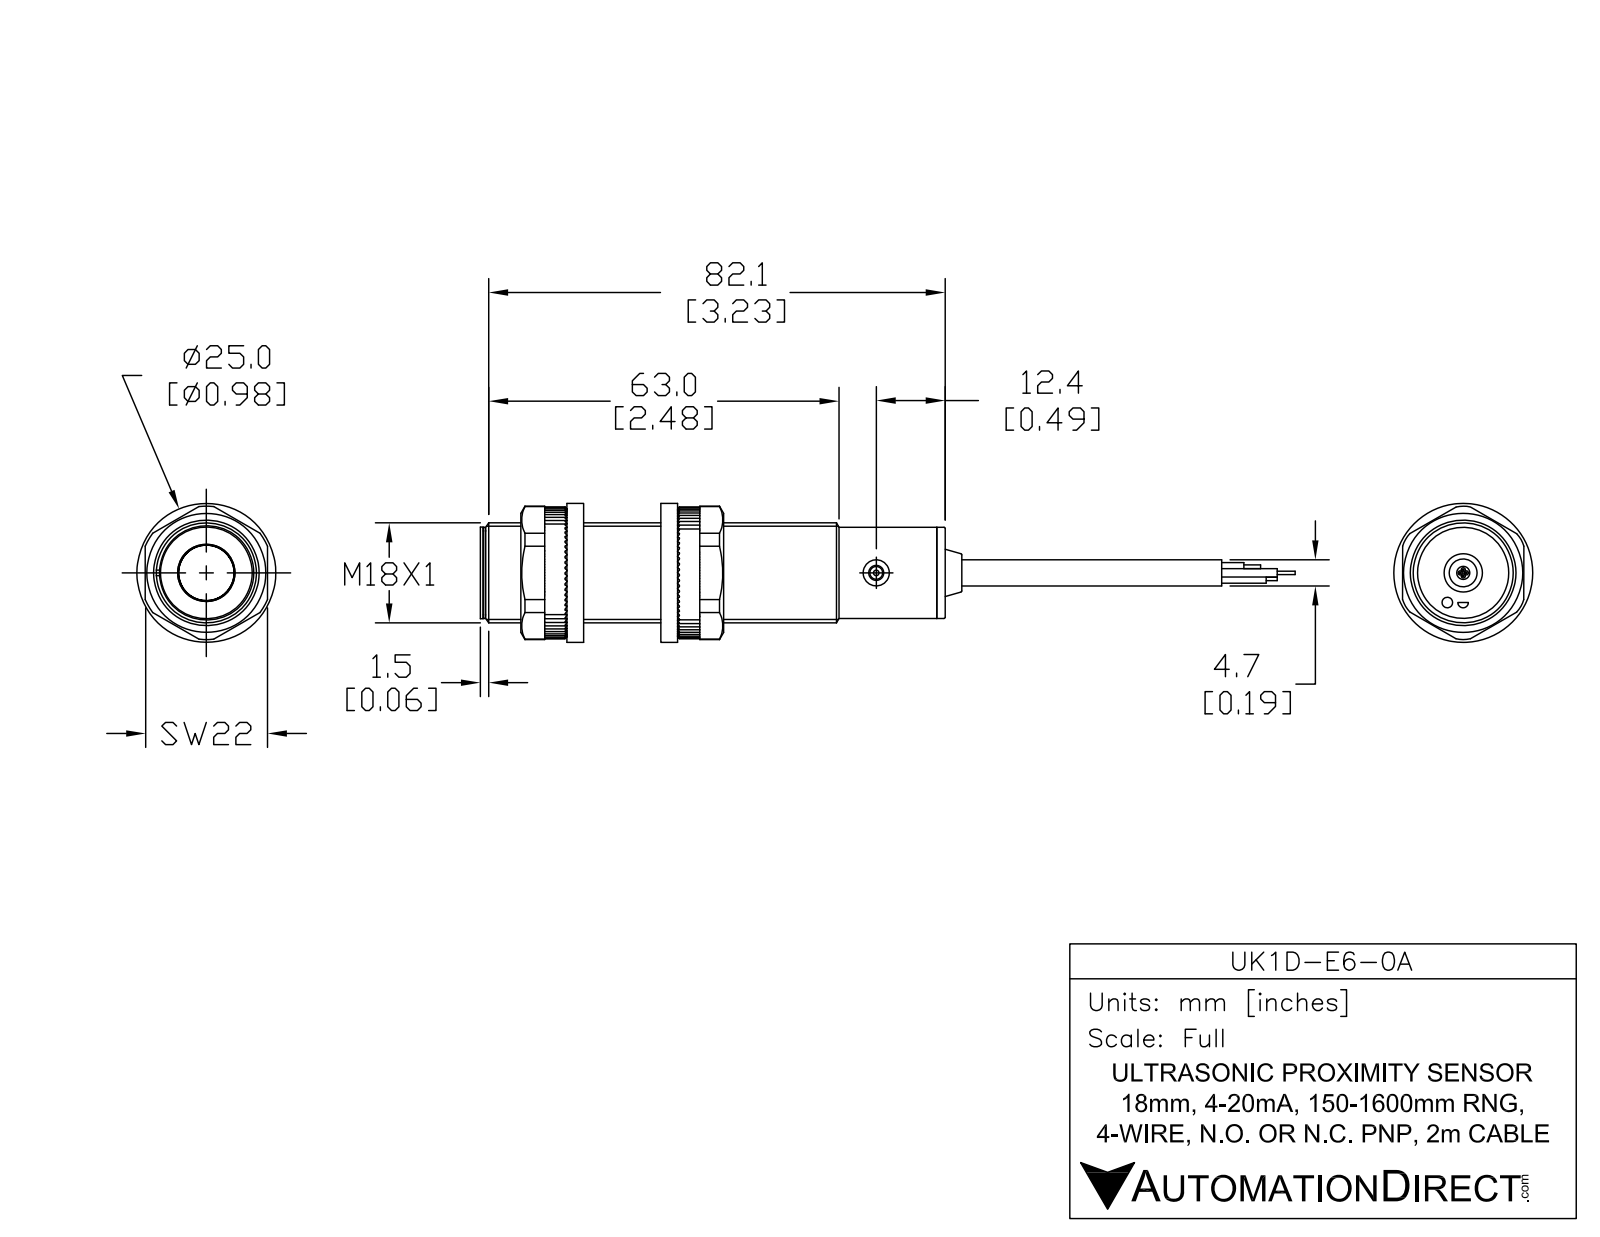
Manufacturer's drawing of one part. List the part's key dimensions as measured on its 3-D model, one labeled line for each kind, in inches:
Part name (STEP PRODUCT): UK1D-E6-0A
STEP written by: SolidWorks 2017 (AUTOMOTIVE_DESIGN)
Units: inches
Bodies: 6 solids, 55 faces (17 planar, 24 cylindrical, 14 other)
Overall size (bounding box): 4.832 × 0.709 × 0.709
Volume: 1.285 in³ · Surface area: 10.69 in²
Round holes (diameter × count): ⌀0.185 ×2, ⌀0.106 ×1
Round bosses / shafts (diameter × count): ⌀0.709 ×1, ⌀0.646 ×1, ⌀0.622 ×1, ⌀0.374 ×1, ⌀0.189 ×1, ⌀0.091 ×1
Main face-to-face distances: 3.193, 3.252, 0.059, 0.039, 3.232, 3.291, 0.041, 3.234, 3.293, 3.257
